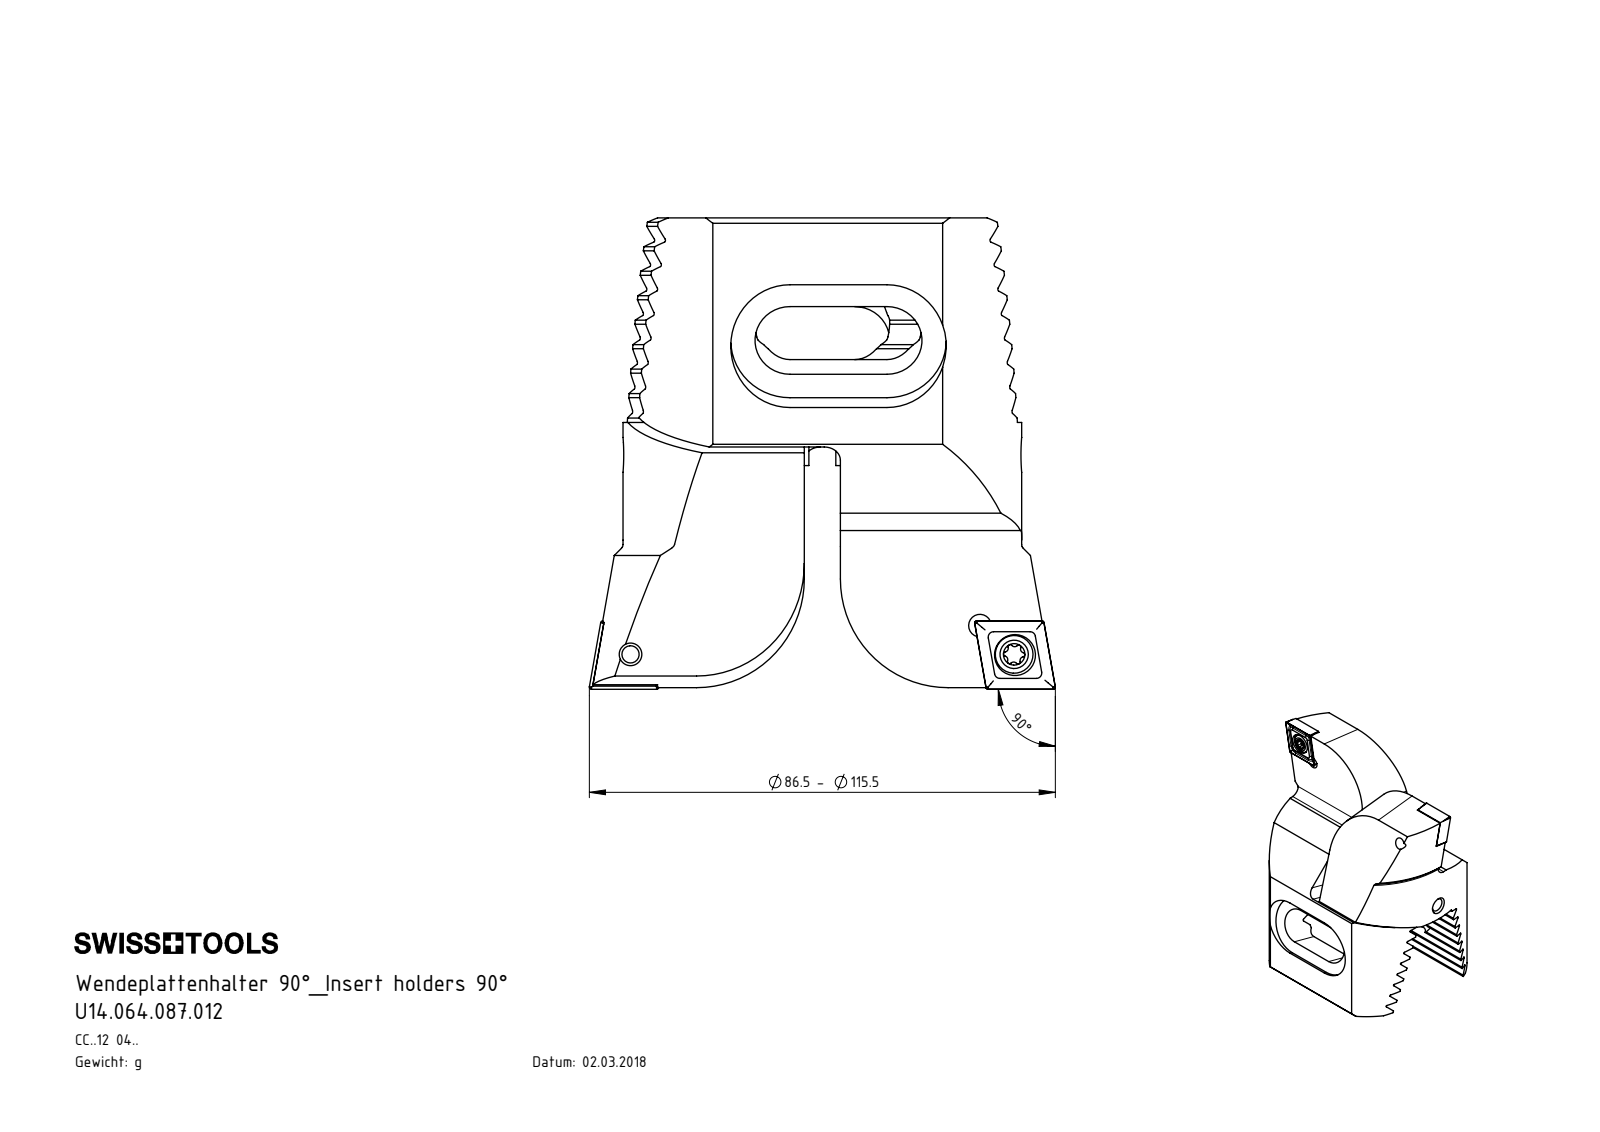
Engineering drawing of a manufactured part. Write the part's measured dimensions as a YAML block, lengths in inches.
part_name: "Z72-ER3.001.030; CCMT120404; WCC-ER2.001.010_A; Z72-WCC.001.050_A (+1 more)"
step_written_by: "SolidWorks 2017 (AUTOMOTIVE_DESIGN)"
units: inches
bodies: {solids: 8, faces: 352, planar: 178, cylindrical: 92, other: 82}
overall_size: [3.443, 3.406, 2.283]
volume: 8.926
surface_area: 59.16
round_holes:
  - {diameter: 0.165, count: 4}
  - {diameter: 0.039, count: 2}
  - {diameter: 0.217, count: 2}
  - {diameter: 0.299, count: 2}
  - {diameter: 0.197, count: 1}
round_bosses_or_shafts:
  - {diameter: 0.276, count: 2}
  - {diameter: 0.197, count: 2}
  - {diameter: 0.236, count: 1}
  - {diameter: 0.157, count: 1}
partial_cylinders:
  - {radius: 0.013, count: 16}
  - {radius: 0.015, count: 12}
  - {radius: 0.039, count: 8}
  - {radius: 0.027, count: 6}
  - {radius: 0.027, count: 6}
  - {radius: 0.118, count: 4}
  - {radius: 0.256, count: 4}
  - {radius: 0.433, count: 4}
face_to_face_distances: [0.16, 0.32, 0.481, 0.641, 1.13, 1.154, 0.962, 0.036, 0.802, 2.283]
hole_center_spacings: [0.327, 0.335, 0.591, 2.562, 2.569, 2.81, 1.141, 2.303]
